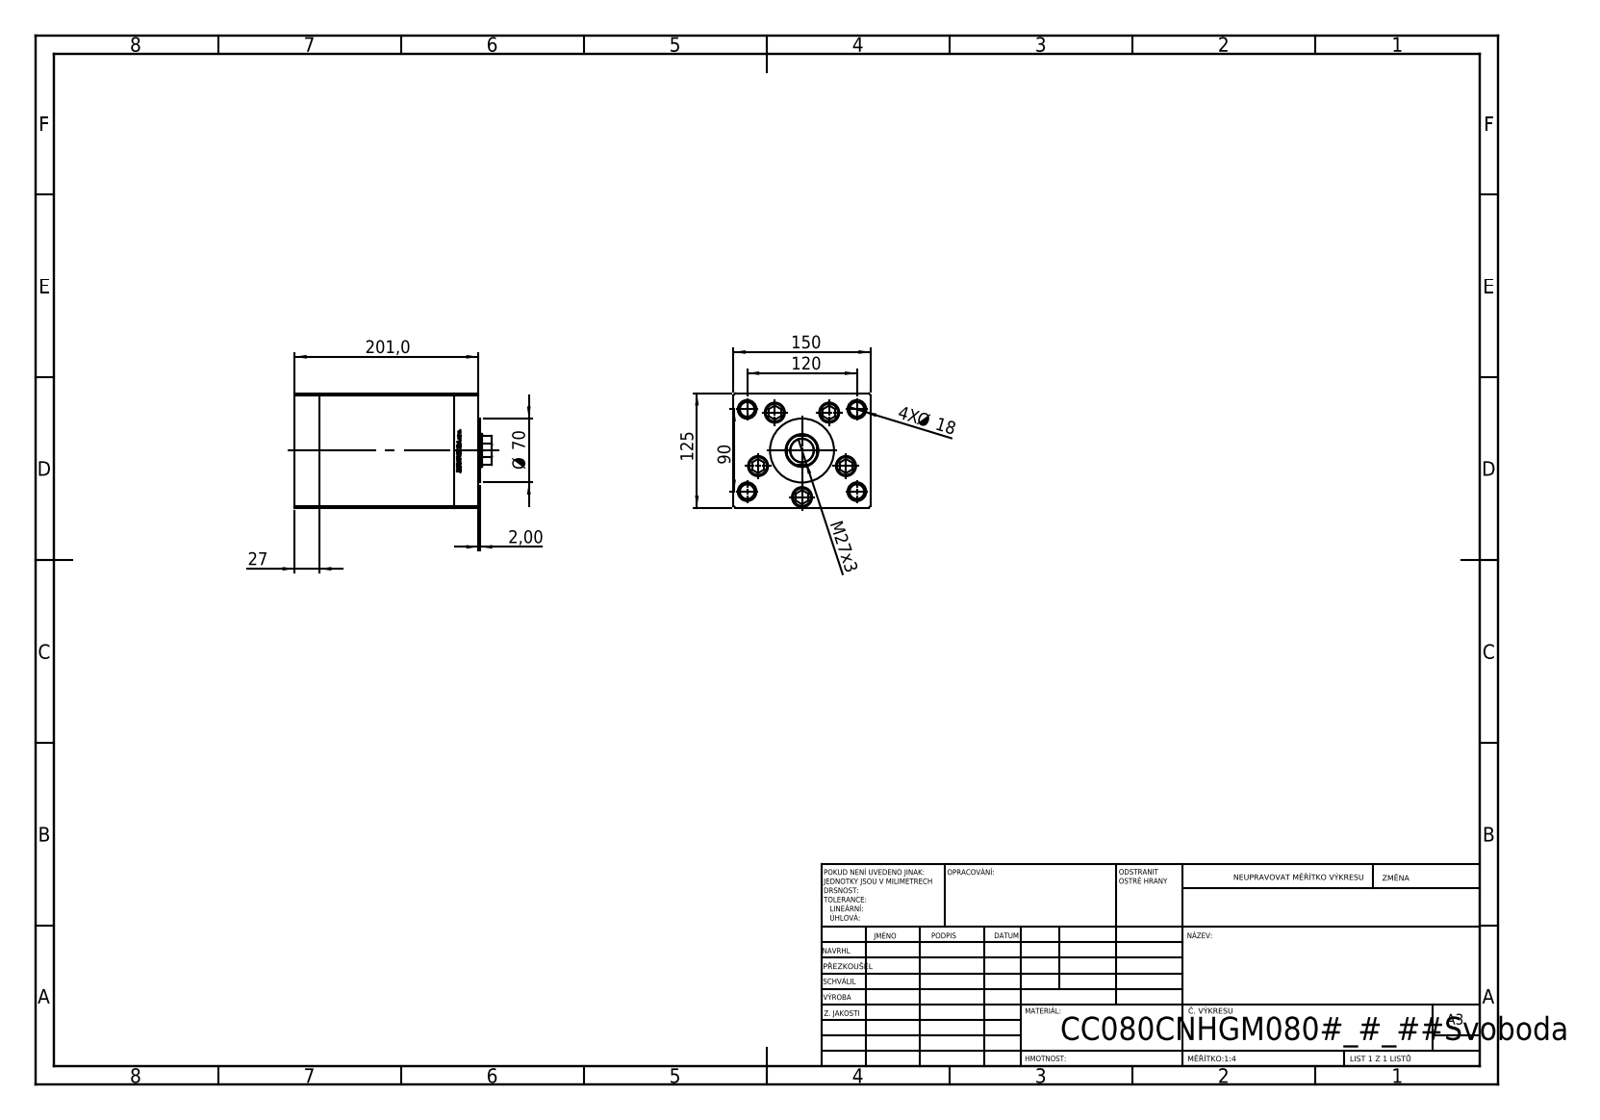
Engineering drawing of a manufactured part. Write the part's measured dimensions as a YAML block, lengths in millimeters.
part_name: "V220C_VC_C; V220C_C MIDDLE; V220C FRONT; V220C BACK_C (+1 more)"
step_written_by: "SolidWorks 2019 (CONFIG_CONTROL_DESIGN)"
units: millimeters
bodies: {solids: 13, faces: 1186, planar: 545, cylindrical: 179, other: 462}
overall_size: [216, 150, 125]
volume: 3120000
surface_area: 380247
round_holes:
  - {diameter: 17.5, count: 9}
  - {diameter: 22, count: 5}
  - {diameter: 2, count: 4}
  - {diameter: 13.16, count: 4}
  - {diameter: 16, count: 4}
  - {diameter: 20.5, count: 4}
  - {diameter: 21, count: 1}
  - {diameter: 25.5, count: 1}
  - {diameter: 36, count: 1}
round_bosses_or_shafts:
  - {diameter: 8, count: 5}
  - {diameter: 21, count: 4}
  - {diameter: 80, count: 1}
  - {diameter: 70, count: 1}
partial_cylinders:
  - {radius: 0.93, count: 2}
  - {radius: 17.5, count: 1}
face_to_face_distances: [27, 174, 147, 125, 150, 33.5, 201, 6.5, 167.5, 140.5]
hole_center_spacings: [51, 75, 30.43, 30.48, 58.89, 60.3, 61.25, 63.14]
